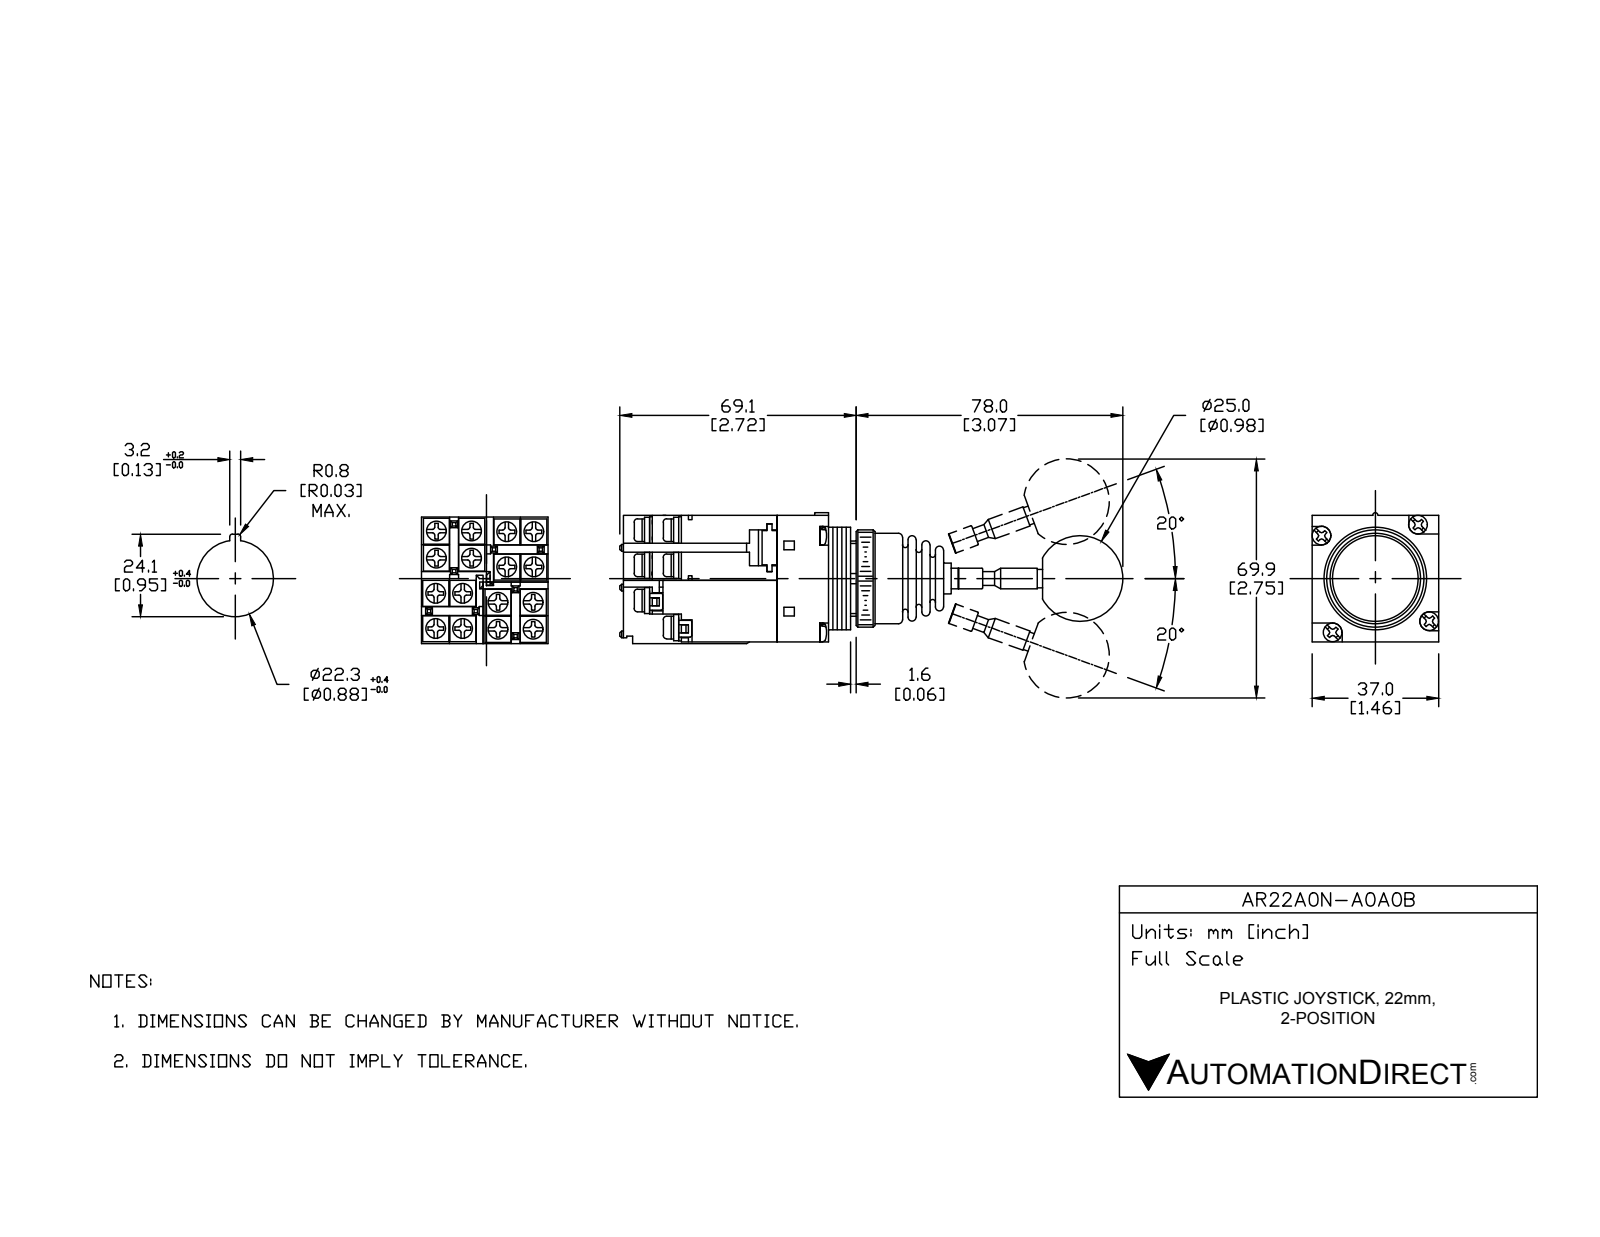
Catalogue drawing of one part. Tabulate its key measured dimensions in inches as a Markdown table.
| quantity | value |
| --- | --- |
| part name | AR22A0N-A0A0B |
| STEP written by | SolidWorks 2017 (AUTOMOTIVE_DESIGN) |
| units | inches |
| bodies | 20 solids, 327 faces (189 planar, 56 cylindrical, 82 other) |
| overall size | 5.752 × 1.457 × 1.457 |
| volume | 3.804 in³ |
| surface area | 46.37 in² |
| round holes (diameter × count) | 0.244 × 1, 0.63 × 1, 0.886 × 1, 1.024 × 1 |
| round bosses / shafts (diameter × count) | 0.228 × 4, 0.157 × 4, 1.181 × 1, 1.102 × 1, 0.866 × 1, 0.236 × 1 |
| partial cylindrical surfaces (radius × count) | 0.11 × 2, 0.118 × 2 |
| main face-to-face distances | 0.738, 0.719, 0.051, 1.457, 0.102, 0.154, 0.02, 0.591, 0.205, 0.407 |
